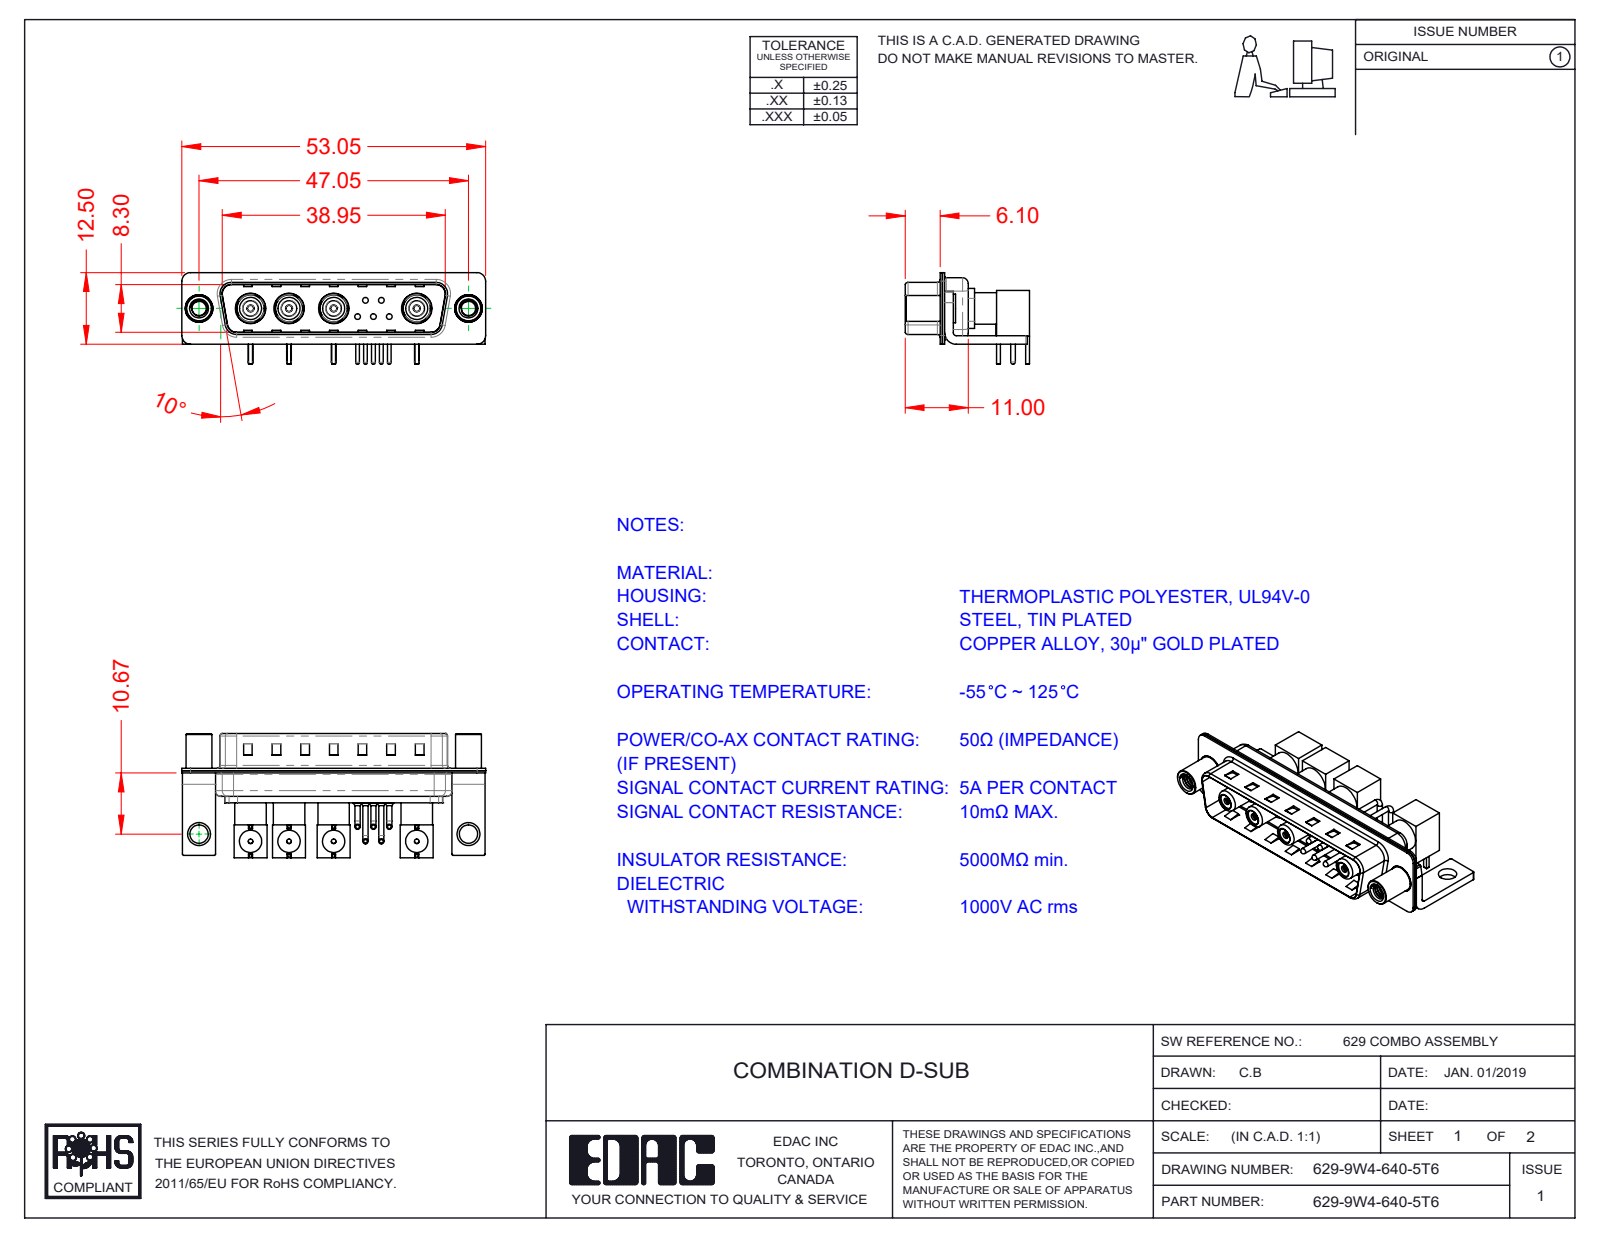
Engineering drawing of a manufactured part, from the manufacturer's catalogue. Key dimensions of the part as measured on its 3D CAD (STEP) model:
Part name (STEP PRODUCT): Co-Ax Jack Assy_RA; Co-Ax Jack_RA PC Tail; 629Combo Housing_9W4; 629-9W4-640-5T6 (+8 more)
STEP written by: SolidWorks 2020 (CONFIG_CONTROL_DESIGN)
Units: millimetres
Bodies: 40 solids, 1632 faces (741 planar, 657 cylindrical, 234 other)
Overall size (bounding box): 53.05 × 21.71 × 16
Volume: 4 281 mm³ · Surface area: 11 553 mm²
Round holes (diameter × count): ⌀1.6 ×9, ⌀2.5 ×6, ⌀0.75 ×5, ⌀2 ×5, ⌀0.8 ×4, ⌀1.1 ×4, ⌀1.2 ×4, ⌀1.5 ×4, ⌀2.7 ×4, ⌀3.1 ×4, ⌀3.4 ×4, ⌀3.9 ×4
Round bosses / shafts (diameter × count): ⌀0.9 ×10, ⌀0.8 ×8, ⌀1.5 ×5, ⌀1 ×5, ⌀0.65 ×5, ⌀5.5 ×4, ⌀5.2 ×4, ⌀4.8 ×4
Partial cylindrical surfaces — rounded edges, fillets, slot ends (radius × count): R0.25 ×16, R1.5 ×16, R2 ×13, R0.5 ×9, R1.6 ×8, R1.01 ×5, R0.6 ×4, R0.65 ×4
Main face-to-face distances: 0.4, 0.8, 9.5, 1.5, 5.75, 9.1, 8.7, 1.4, 9.9, 0.35
Hole centre spacings: 14.51, 14.52, 6.72, 7.79, 22.3, 29.02, 3.16, 14.5
